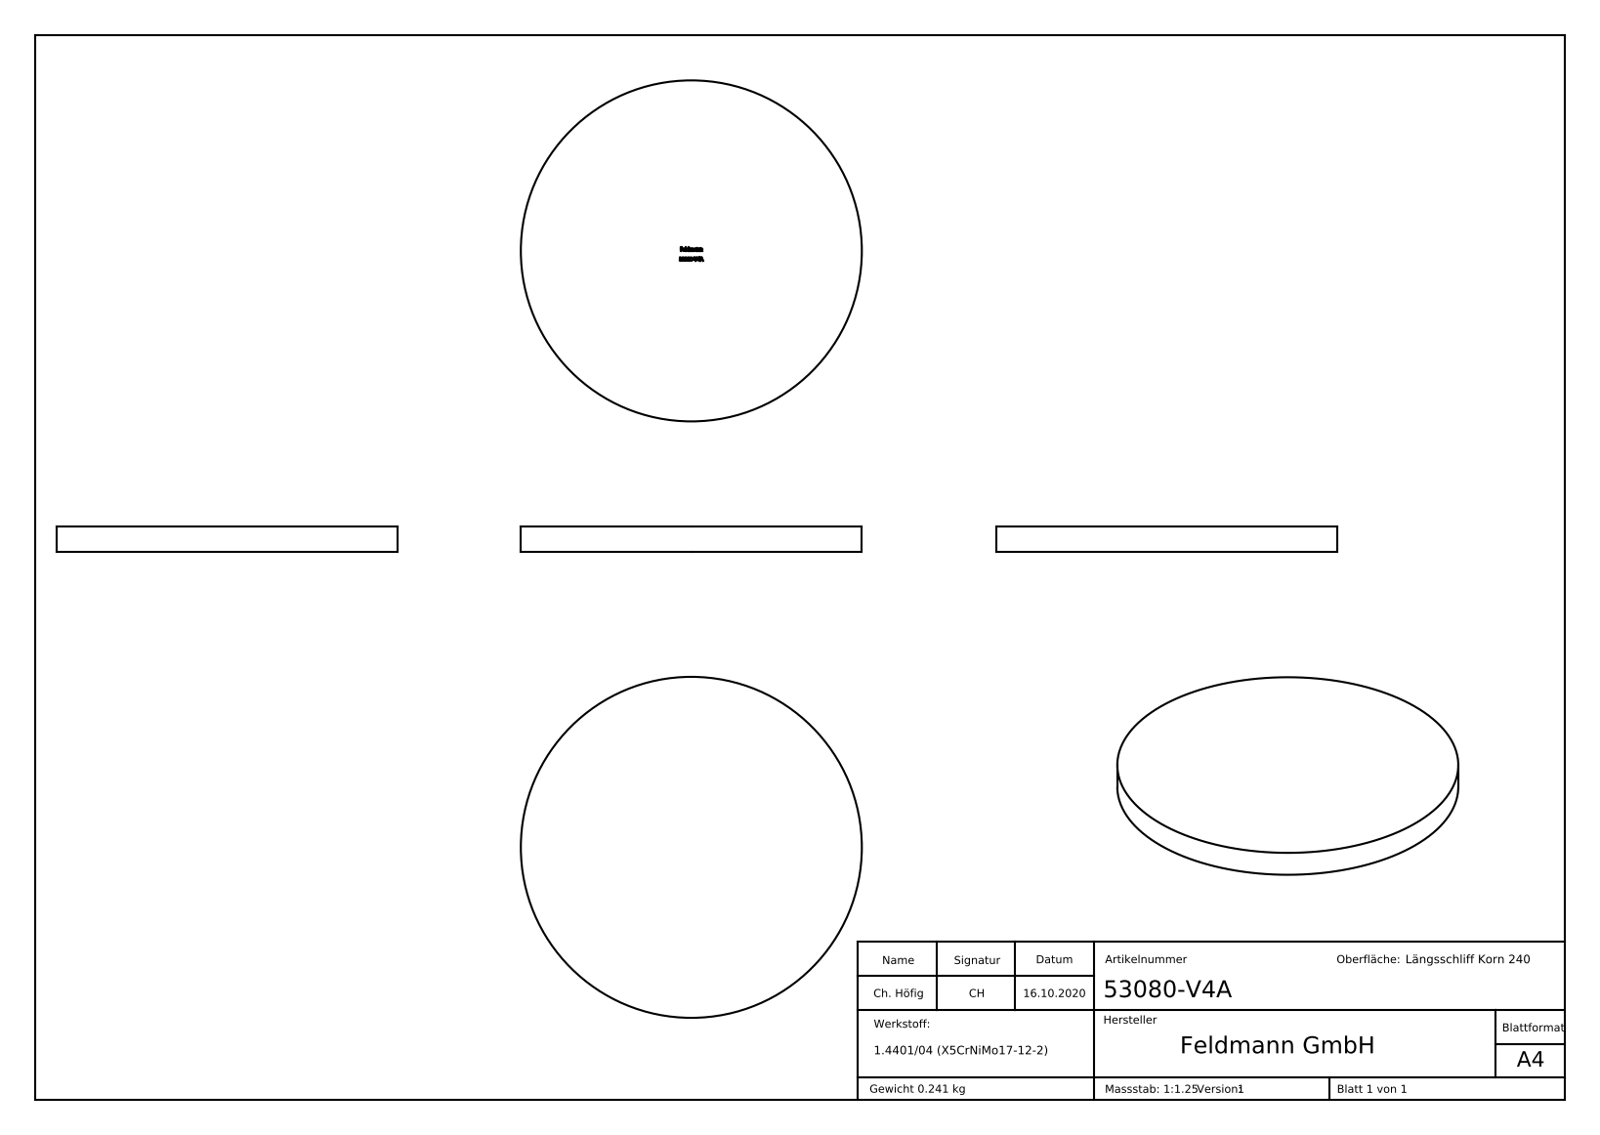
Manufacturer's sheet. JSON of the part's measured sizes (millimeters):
{"part_name": "53080-V4A", "step_written_by": "SolidWorks 2018 (CONFIG_CONTROL_DESIGN)", "units": "millimeters", "bodies": {"solids": 1, "faces": 233, "planar": 126, "cylindrical": 2, "other": 105}, "overall_size": [80, 80, 6], "volume_mm3": 30159, "surface_area_mm2": 11567, "round_bosses_or_shafts": [[80, 1]], "face_to_face_distances": [6, 5.9, 1.78, 0.44, 2.45, 0.83, 0.99, 2.77, 2.38, 0.67]}
